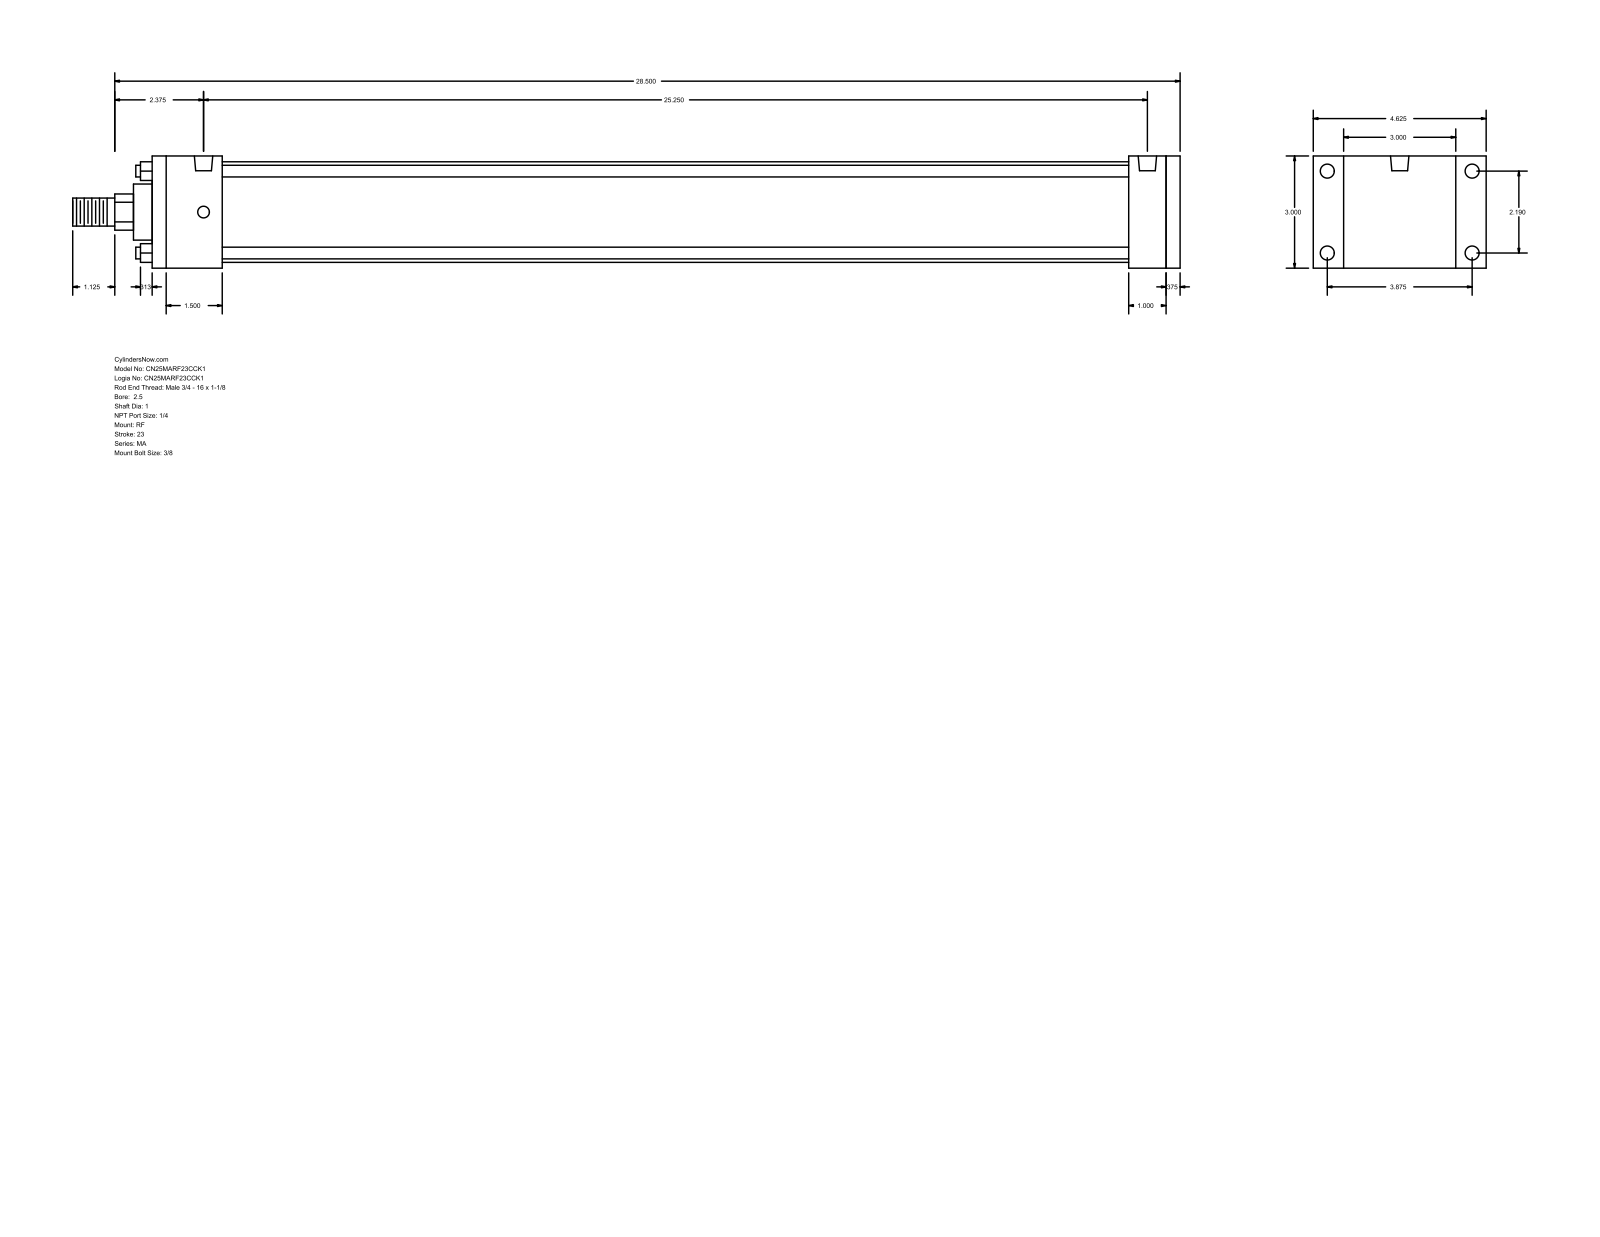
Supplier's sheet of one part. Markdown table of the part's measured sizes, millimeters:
| quantity | value |
| --- | --- |
| part name | MA_RF__0250_1 |
| STEP written by | GSSL Pune (CONFIG_CONTROL_DESIGN) |
| units | millimeters |
| bodies | 0 solids, 92 faces (64 planar, 28 cylindrical, 0 other) |
| overall size | 752.48 × 117.47 × 76.2 |
| round holes (diameter × count) | 7.94 × 4, 9.53 × 4, 12.49 × 2 |
| round bosses / shafts (diameter × count) | 7.94 × 4, 68.33 × 1, 38.1 × 1, 25.4 × 1, 19.05 × 1 |
| partial cylindrical surfaces (radius × count) | 12.29 × 1 |
| main face-to-face distances | 76.2, 698.5, 688.98, 9.52, 25.4, 47.63, 663.58, 615.95, 641.35, 650.87 |
| hole center spacings | 55.62, 98.42, 113.05, 641.34 |
